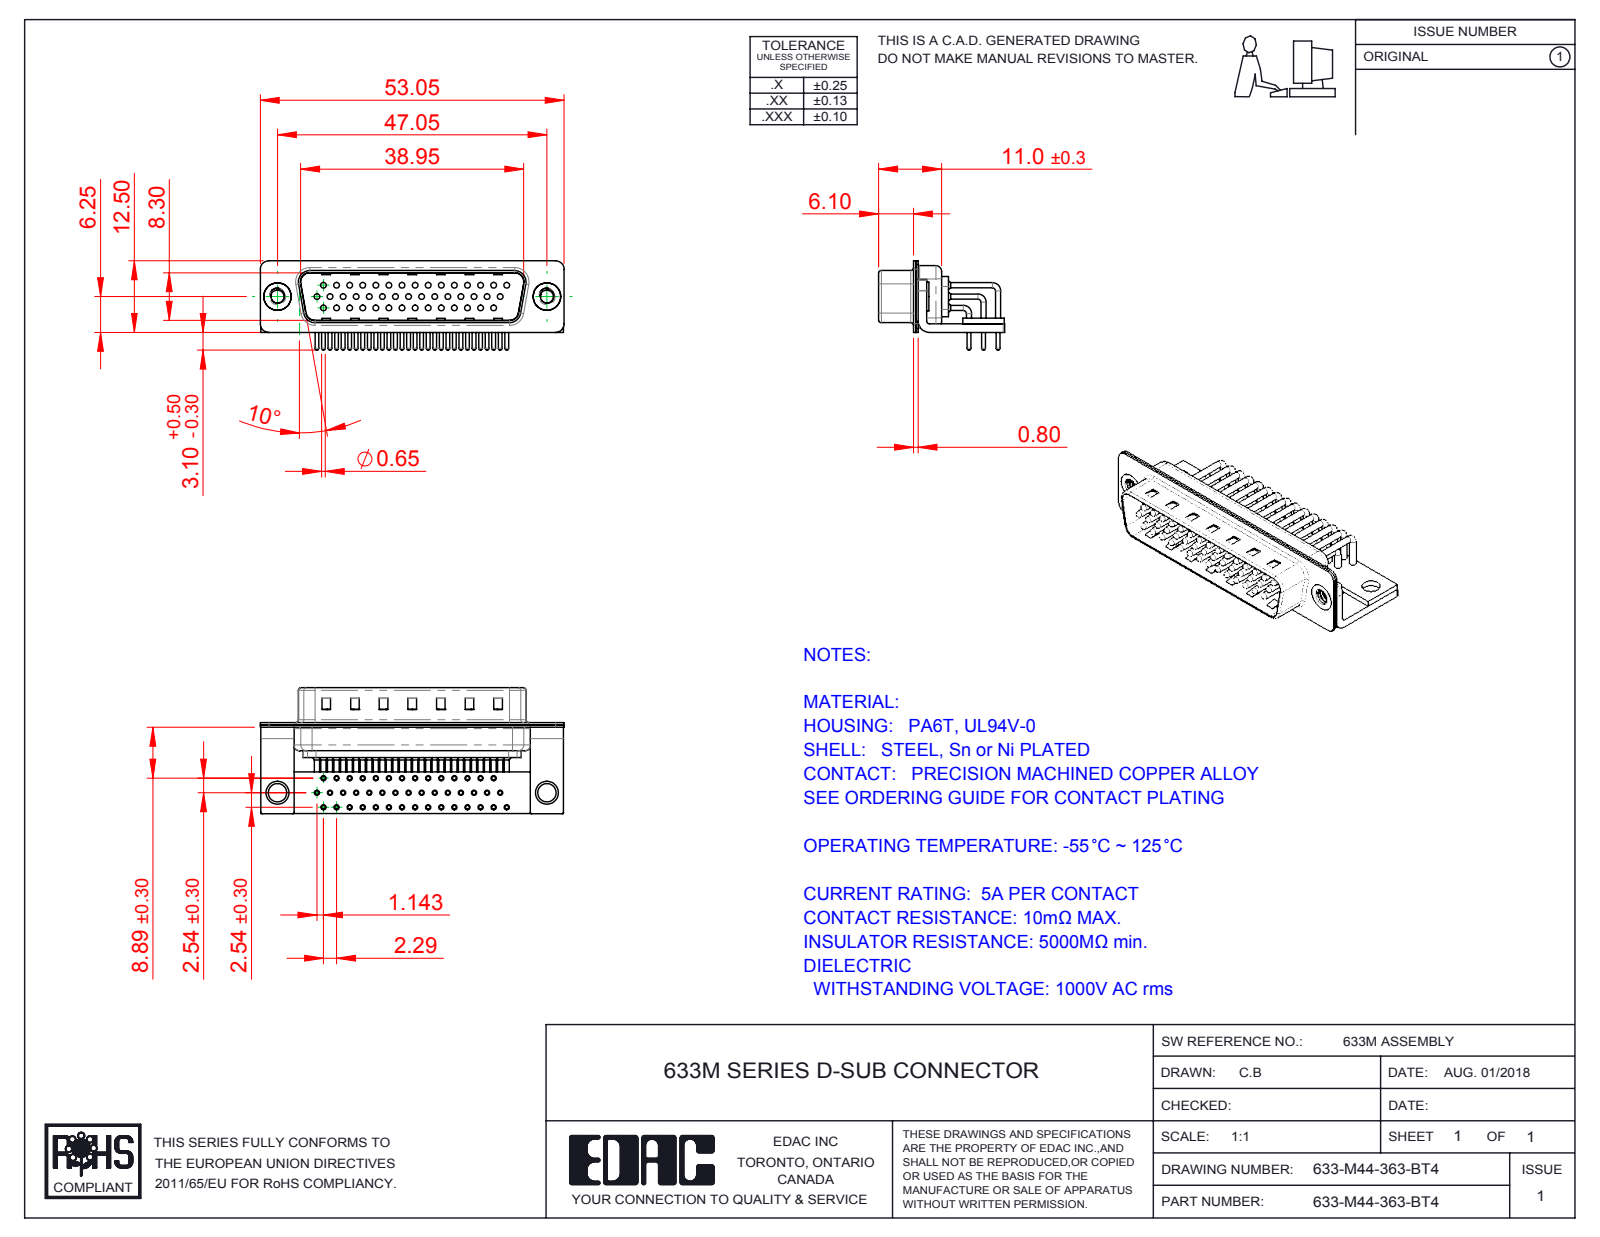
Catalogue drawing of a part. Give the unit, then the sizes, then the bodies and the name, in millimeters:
Units: millimetres
Overall size (bounding box): 53.05 × 22 × 15.6
Round holes (diameter × count): ⌀0.9 ×44, ⌀1 ×44, ⌀1.7 ×44, ⌀2 ×44, ⌀2.26 ×2, ⌀3.2 ×2, ⌀4 ×2, ⌀4.8 ×2
Round bosses / shafts (diameter × count): ⌀0.9 ×45, ⌀1.5 ×44, ⌀0.65 ×44, ⌀5 ×2, ⌀4.9 ×2, ⌀1 ×2
Partial cylindrical surfaces — rounded edges, fillets, slot ends (radius × count): R1.01 ×44, R0.25 ×16, R1.5 ×16, R2 ×13, R0.5 ×9, R1.6 ×8, R0.6 ×4, R0.65 ×4
Main face-to-face distances: 0.4, 0.85, 1.5, 1.25, 1, 1.9, 0.8, 9.55, 10.4, 8.3
Hole centre spacings: 2.28, 2.29, 4.57, 6.86, 3.96, 11.43, 8.24, 16
Volume: 3 754 mm³ · Surface area: 11 606 mm²
Bodies: 52 solids, 5354 faces (3013 planar, 1831 cylindrical, 510 other)
Part name (STEP PRODUCT): 633M Shell Rear_44 Contacts; 633M Shell Front_44 Contacts; 633M 4-40 Threaded Rivet_Stabilizer; 633M Stabilizer Bracket (+6 more)
STEP written by: SolidWorks 2016 (CONFIG_CONTROL_DESIGN)
